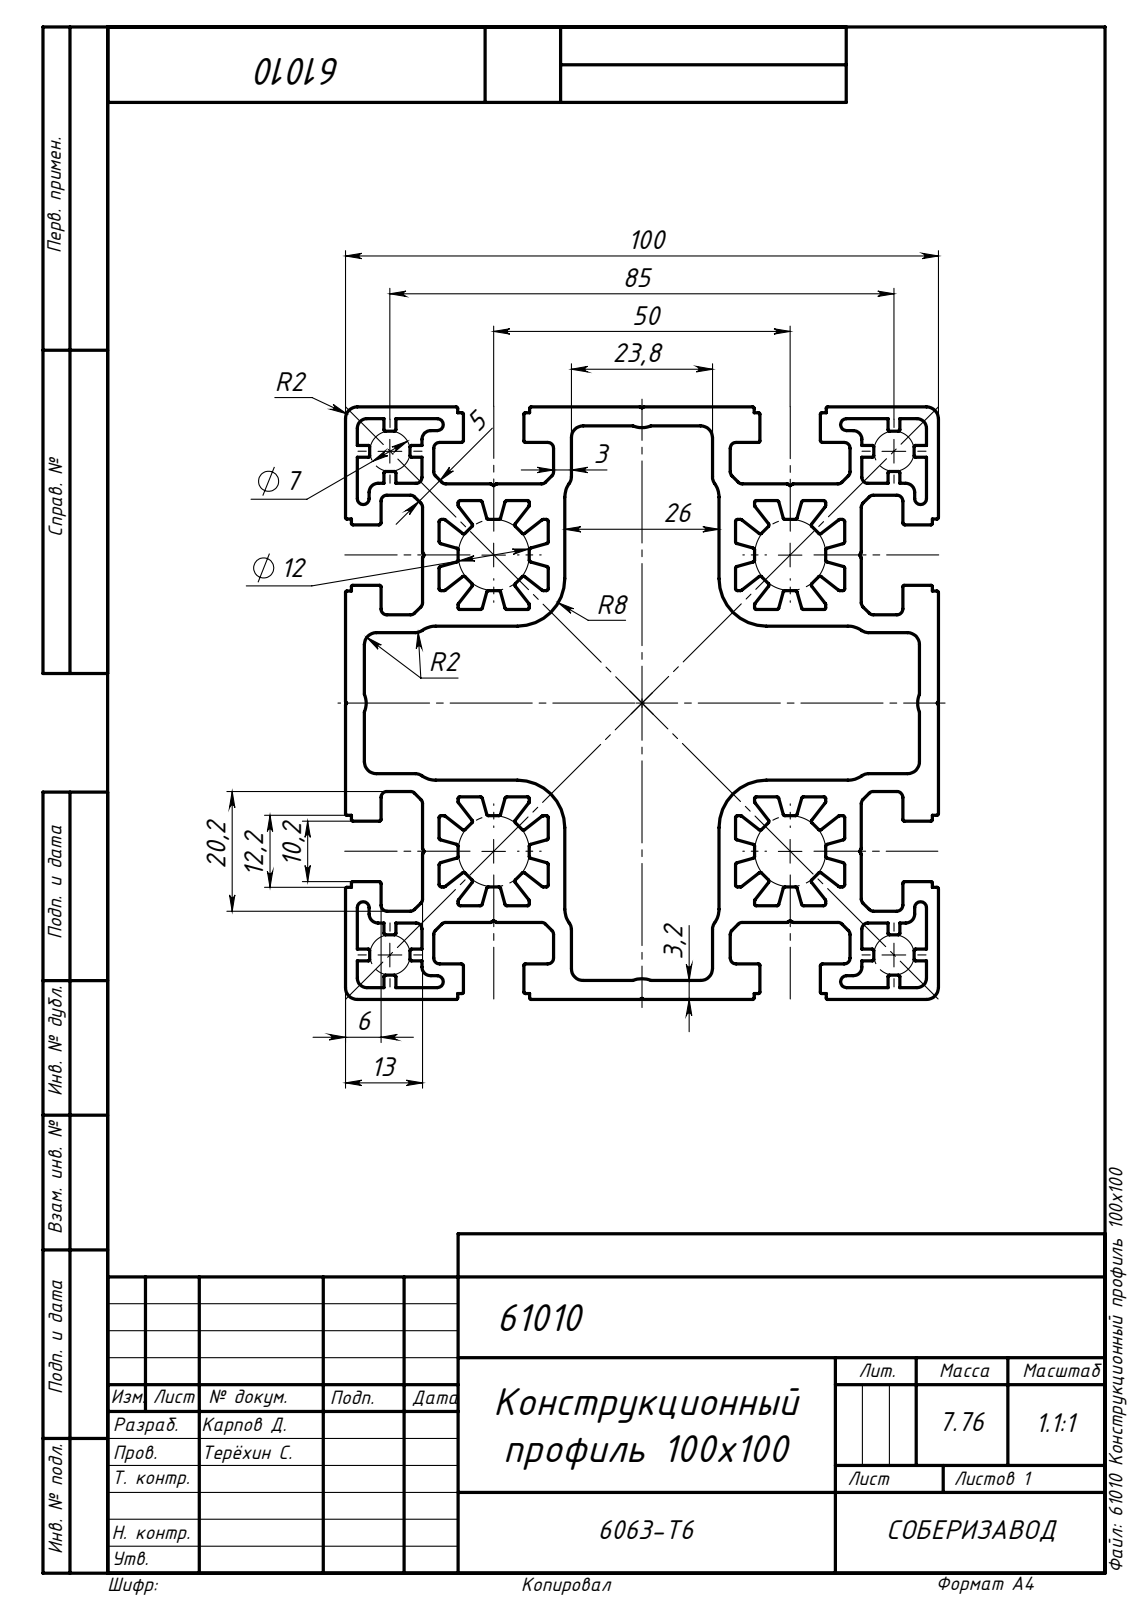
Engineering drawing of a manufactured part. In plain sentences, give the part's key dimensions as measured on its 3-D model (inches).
The part is named "61010 Конструкционный профиль 100х100". Its 3-D file was written by "SolidWorks 2019 (AUTOMOTIVE_DESIGN)". It is 1 solid with 814 faces: 426 planar, 388 cylindrical and 0 other. Overall it measures 39.37 by 3.937 by 3.937 inches. Its volume is 175.4 cubic inches and its surface area 2 824 square inches. Partial cylindrical surfaces (rounded edges, fillets, slot ends): 120 of radius 0.012, 112 of radius 0.01, 60 of radius 0.039, 24 of radius 0.016, 20 of radius 0.079, 12 of radius 0.157, 8 of radius 0.014, 8 of radius 0.059. The main face-to-face distances are 0.11, 1.969, 3.937, 2.354, 0.386, 0.512, 3.425, 1.22, 3.189, 1.457.
